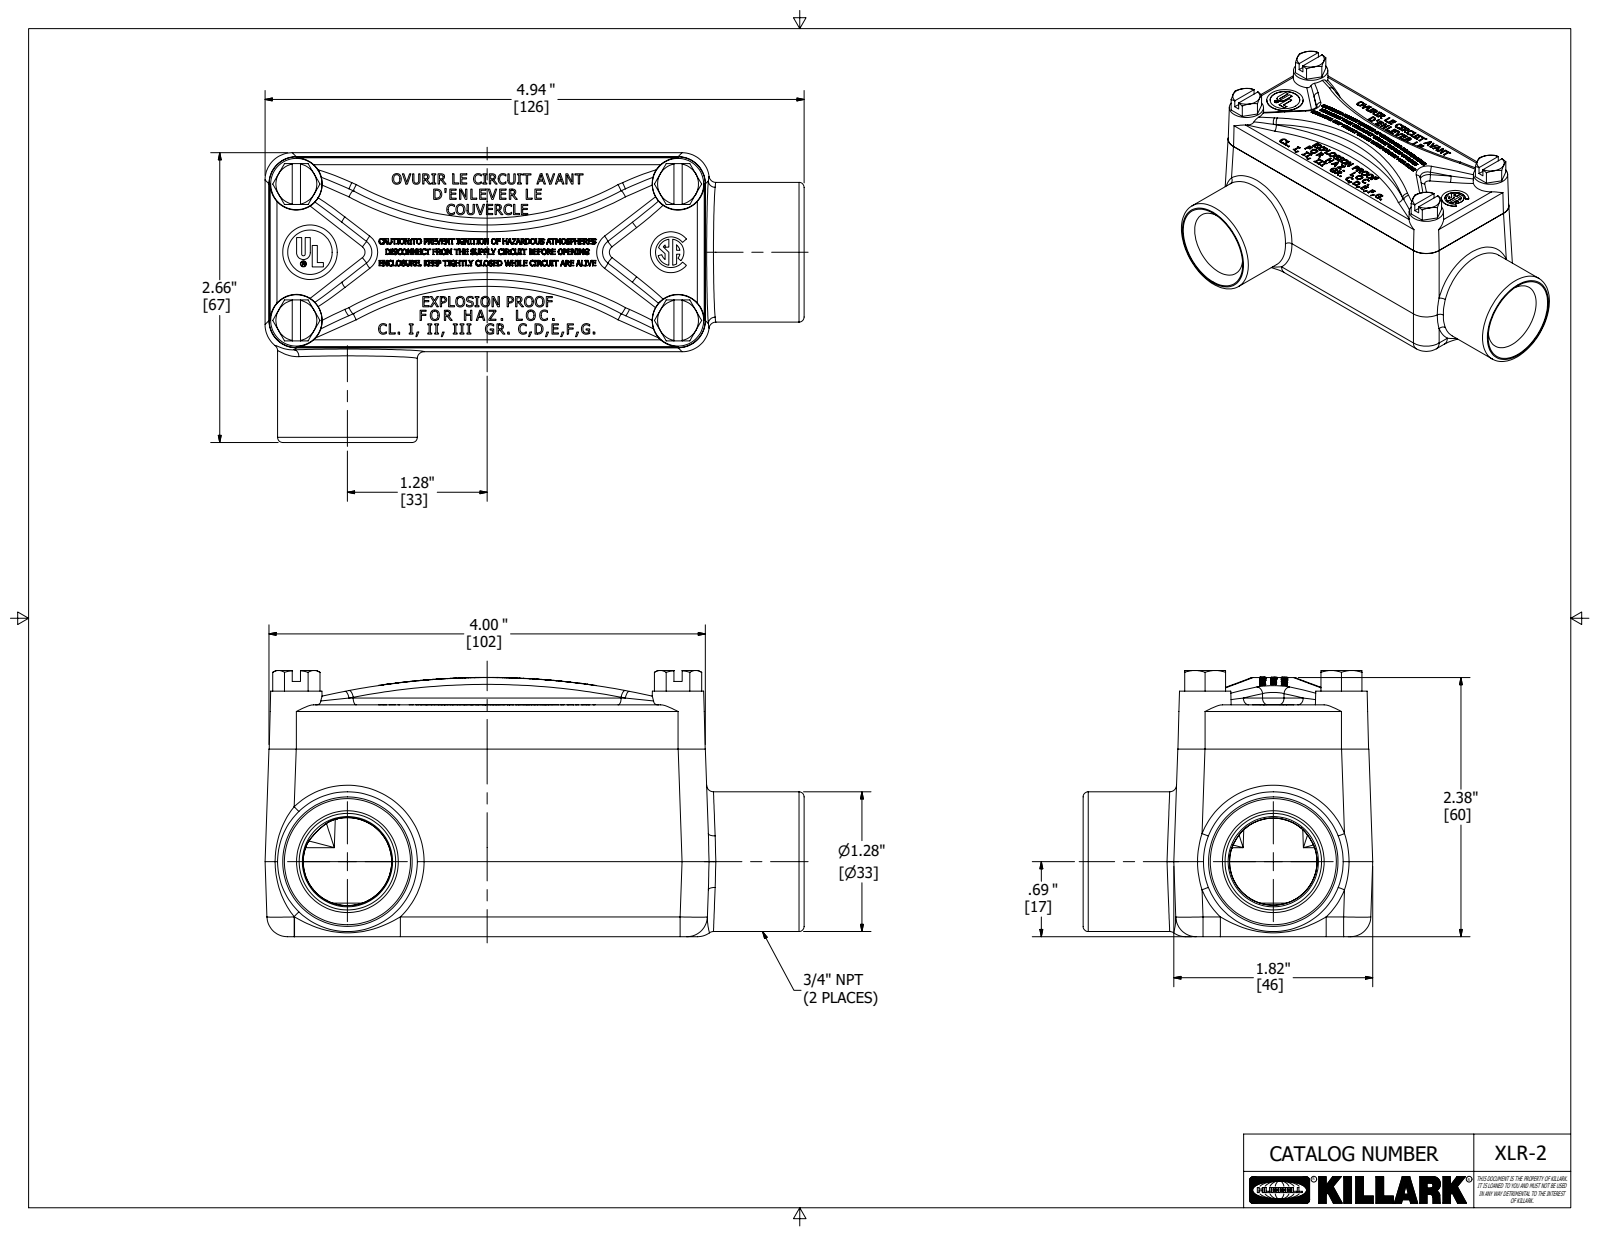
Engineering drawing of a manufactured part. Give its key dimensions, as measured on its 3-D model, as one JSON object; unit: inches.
{"part_name": "cgud71C6uq9w", "step_written_by": "SIEMENS UGS NX 6.0 (CONFIG_CONTROL_DESIGN)", "units": "inches", "bodies": {"solids": 2, "faces": 451, "planar": 87, "cylindrical": 98, "other": 266}, "overall_size": [4.937, 2.656, 2.438], "volume_in3": 8.575, "surface_area_in2": 85.9, "round_bosses_or_shafts": [[1.281, 2]], "partial_cylinders_radius": [[0.062, 35], [0.25, 12], [0.125, 10], [0.156, 10], [0.094, 6], [0.187, 4], [0.406, 2], [0.437, 2]], "face_to_face_distances": [0.156, 1.667, 0.156, 1.75, 1.822, 2.187, 0.437, 1.594, 2.031, 1.511]}
